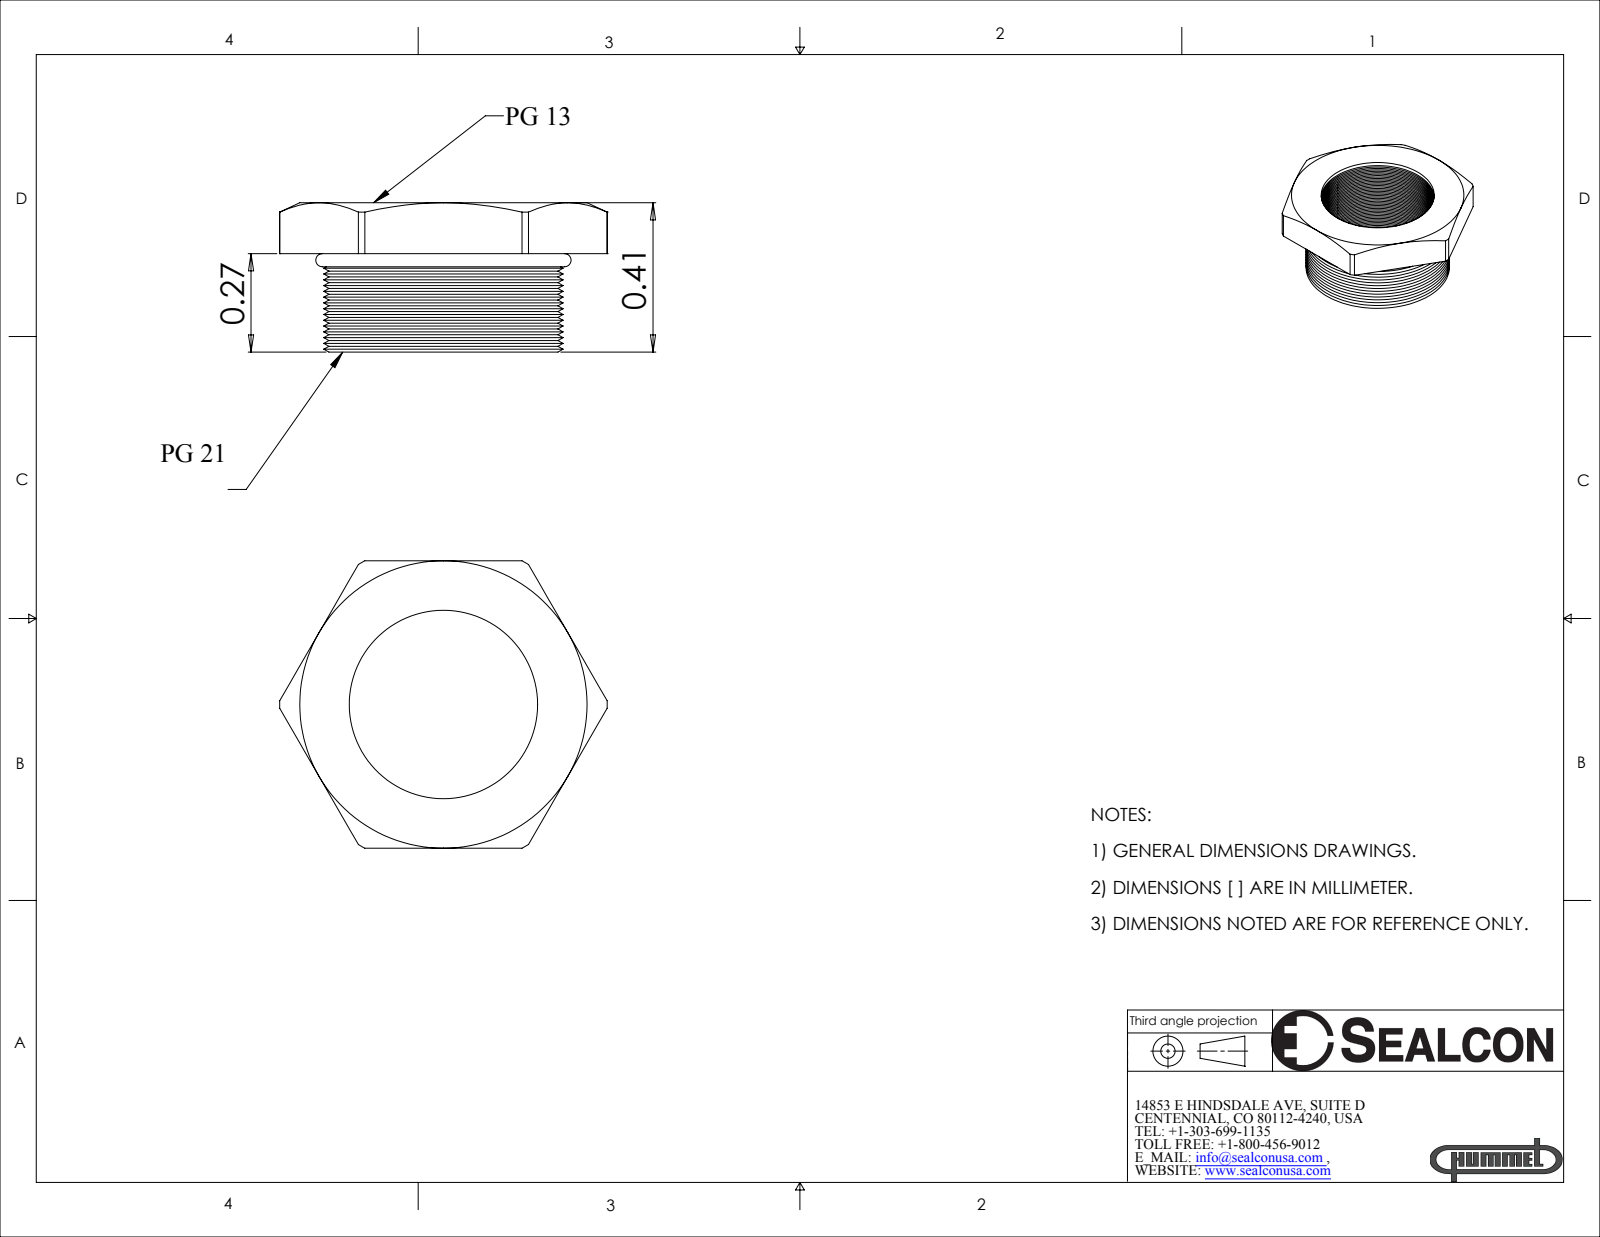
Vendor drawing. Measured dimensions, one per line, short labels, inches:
name: RSD-Ms 1.077.2113.01; HI_RSD-Ms 1.077.2113.01-Reduction; HI_RSD-Ms 1.077.2113.01-O-Ring
written by: PARTsolutions (CONFIG_CONTROL_DESIGN)
unit: in
bodies: 2 solids, 31 faces (9 planar, 9 cylindrical, 13 other)
size: 1.319 × 1.181 × 0.406
volume: 0.234 in³; area: 5.109 in²
holes: 1× ⌀0.75
bosses: 1× ⌀1.114, 1× ⌀1.024
rounds: 1× R0.659
face distances: 0.406, 1.181, 0.13, 0.276
